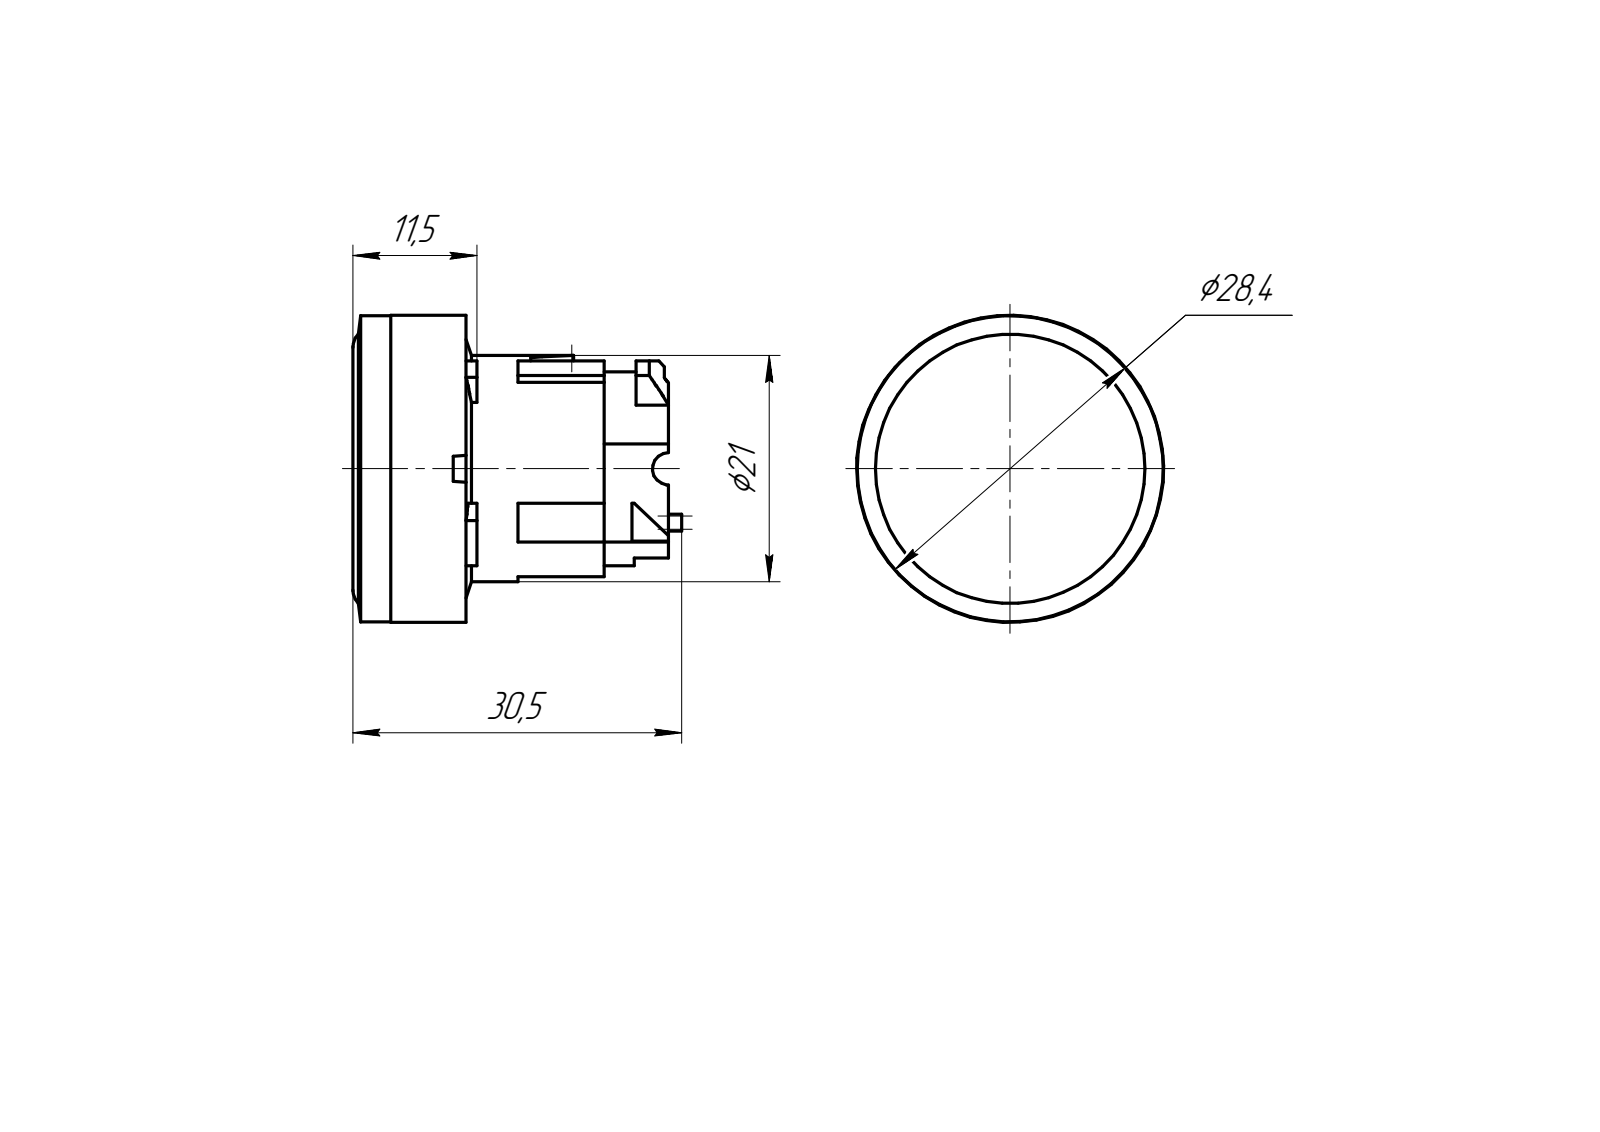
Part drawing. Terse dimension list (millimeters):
name: LA167-B4-BW33C
written by: PRO/ENGINEER BY PARAMETRIC TECHNOLOGY CORPORATION, 2010280 (CONFIG_CONTROL_DESIGN)
unit: mm
bodies: 1 solid, 150 faces (84 planar, 55 cylindrical, 11 other)
size: 30.5 × 28.5 × 28.5
volume: 8 085 mm³; area: 4 734 mm²
bosses: 1× ⌀28.5, 1× ⌀28.4, 1× ⌀21
rounds: 17× R0.2, 4× R0.3, 1× R1.5, 1× R6.9, 1× R8.1, 1× R9, 1× R11, 1× R12
face distances: 5.2, 4.2, 5.8, 14.2, 11.6, 15.8, 16.6, 5, 12.4, 0.8
